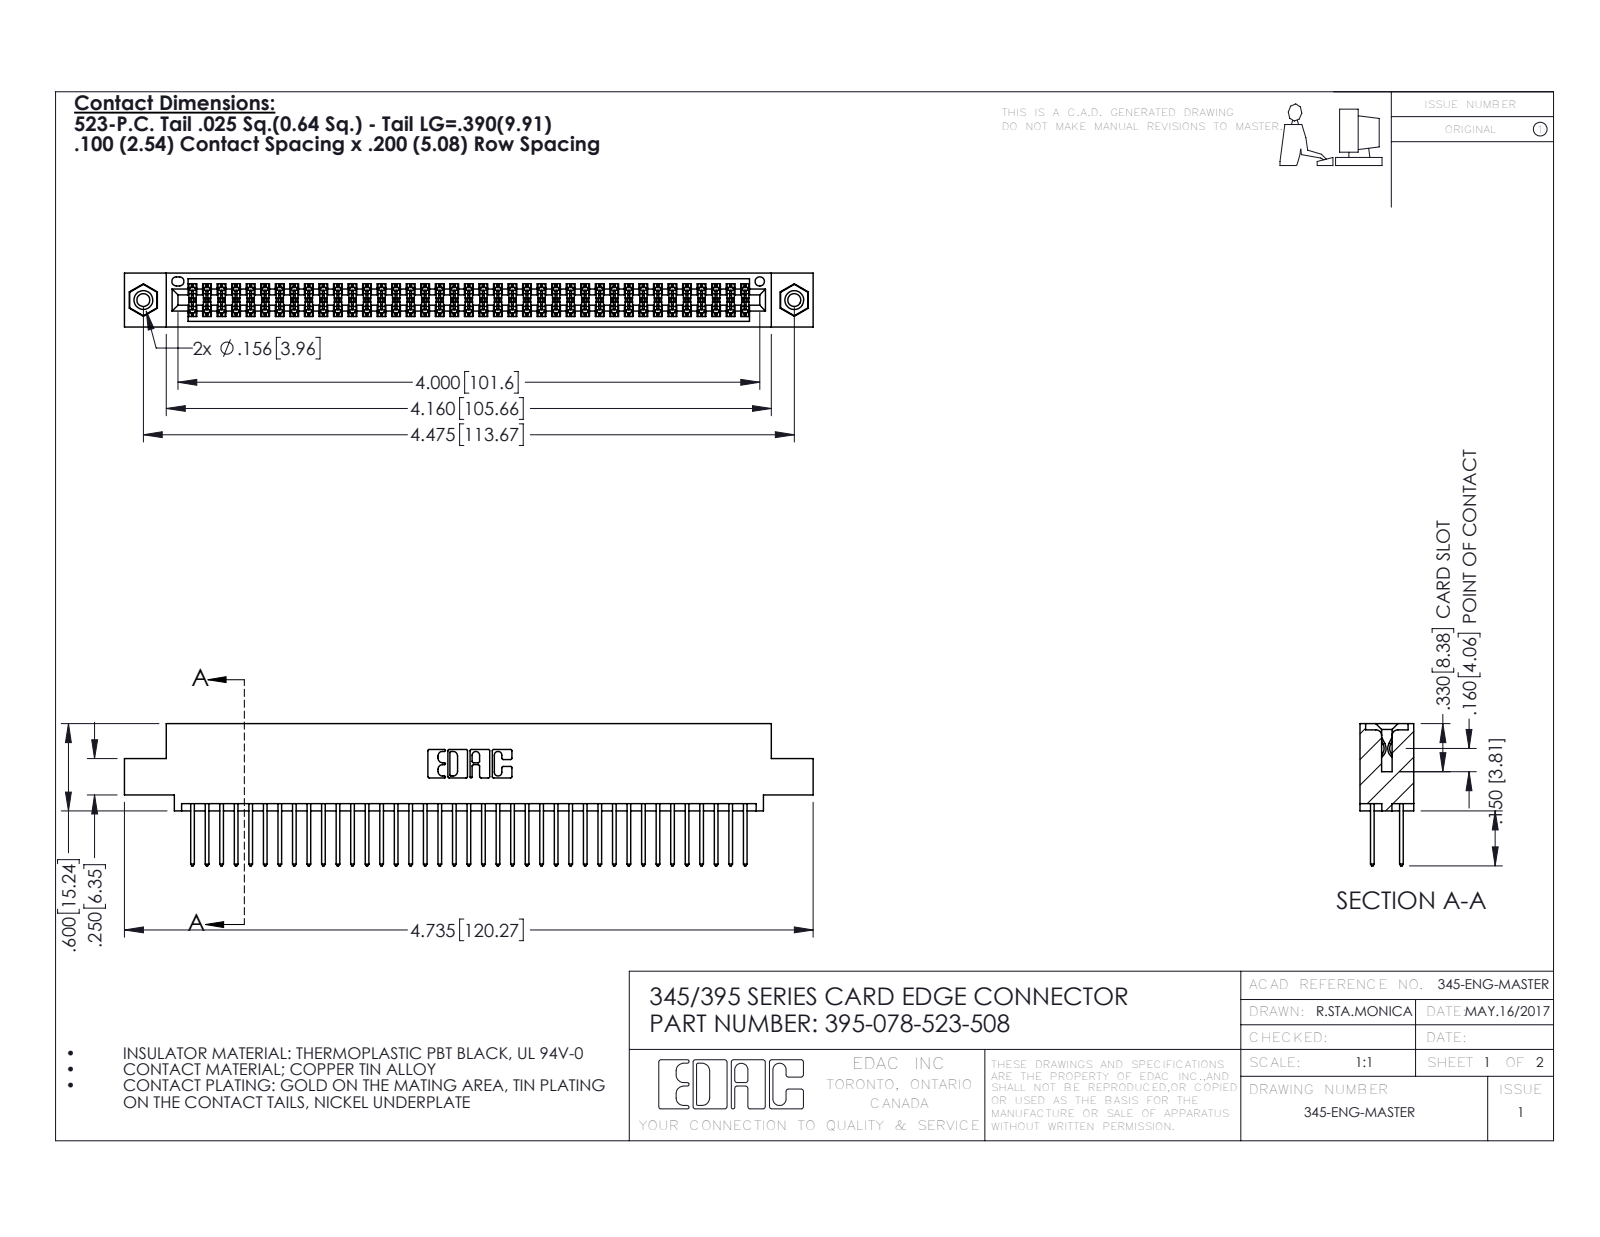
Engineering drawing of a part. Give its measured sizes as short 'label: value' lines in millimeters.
name: 345-292-001_345-293-123; 395-078-523-508; 345-250-001_345-250-003-102; 345 Part_0.110 Offset - 0.156 Dia-TI
written by: SolidWorks 2016 (CONFIG_CONTROL_DESIGN)
unit: mm
bodies: 81 solids, 4090 faces (2690 planar, 1384 cylindrical, 16 other)
size: 120.3 × 24.8 × 9.4
volume: 11 700 mm³; area: 18 110 mm²
holes: 2× ⌀2.3, 2× ⌀3.2, 2× ⌀4, 1× ⌀1.6
bosses: 2× ⌀3.9
rounds: 117× R0.2, 78× R0.3, 22× R0.3, 6× R0.2, 6× R0.8, 3× R0.7, 2× R0.4, 2× R0.5
face distances: 1.8, 7.6, 5.1, 2.5, 6.9, 0.6, 9.4, 5.7, 4.4, 3.8
hole spacings: 6.9, 107.7, 113.7
